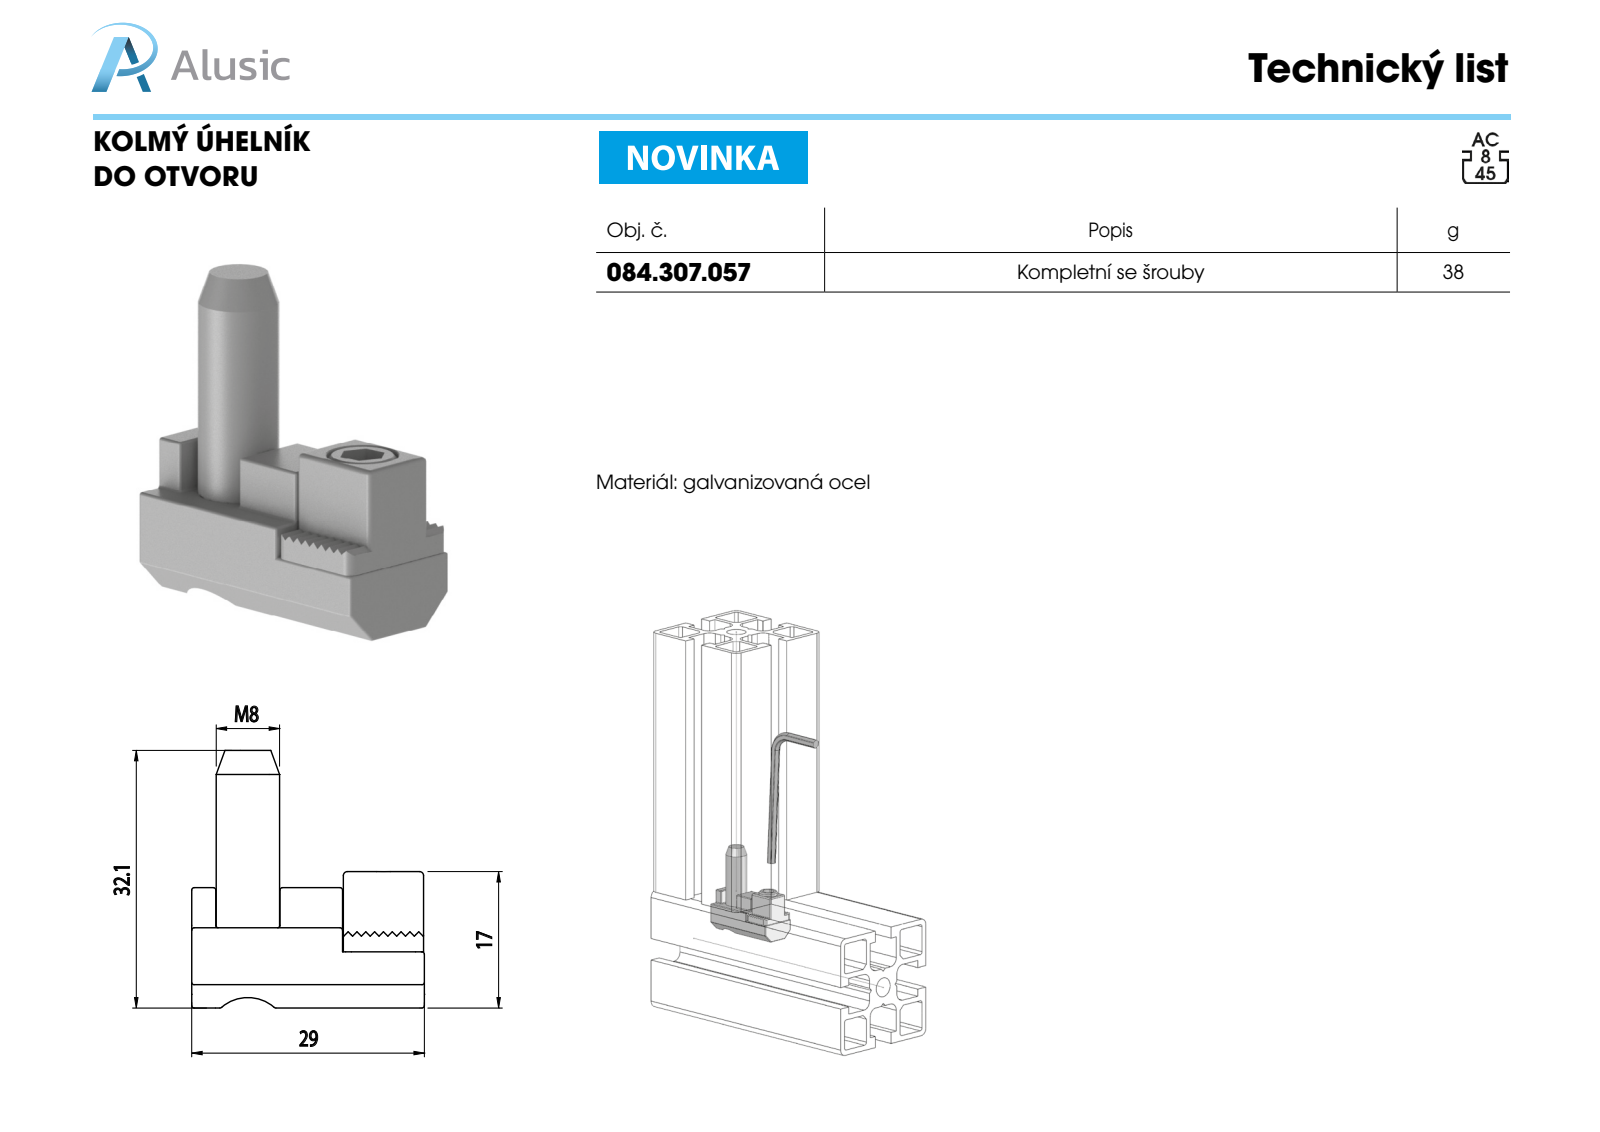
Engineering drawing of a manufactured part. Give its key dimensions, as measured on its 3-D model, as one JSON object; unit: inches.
{"part_name": "Verbindungsschraube; 084.307.057; Spannklotz; Druckschraube M7 (+1 more)", "step_written_by": "SolidWorks 2018 (AUTOMOTIVE_DESIGN)", "units": "inches", "bodies": {"solids": 4, "faces": 247, "planar": 86, "cylindrical": 81, "other": 80}, "overall_size": [1.264, 1.142, 0.528], "volume_in3": 0.318, "surface_area_in2": 6.341, "round_holes": [[0.157, 1], [0.217, 1], [0.276, 1], [0.315, 1], [0.394, 1]], "round_bosses_or_shafts": [[0.386, 1], [0.311, 1]], "partial_cylinders_radius": [[0.012, 41], [0.02, 8], [0.039, 4]], "face_to_face_distances": [0.106, 0.421, 0.315, 0.394, 0.528, 0.398, 0.276, 0.118, 0.311, 0.157], "hole_center_spacings": [0.665]}
